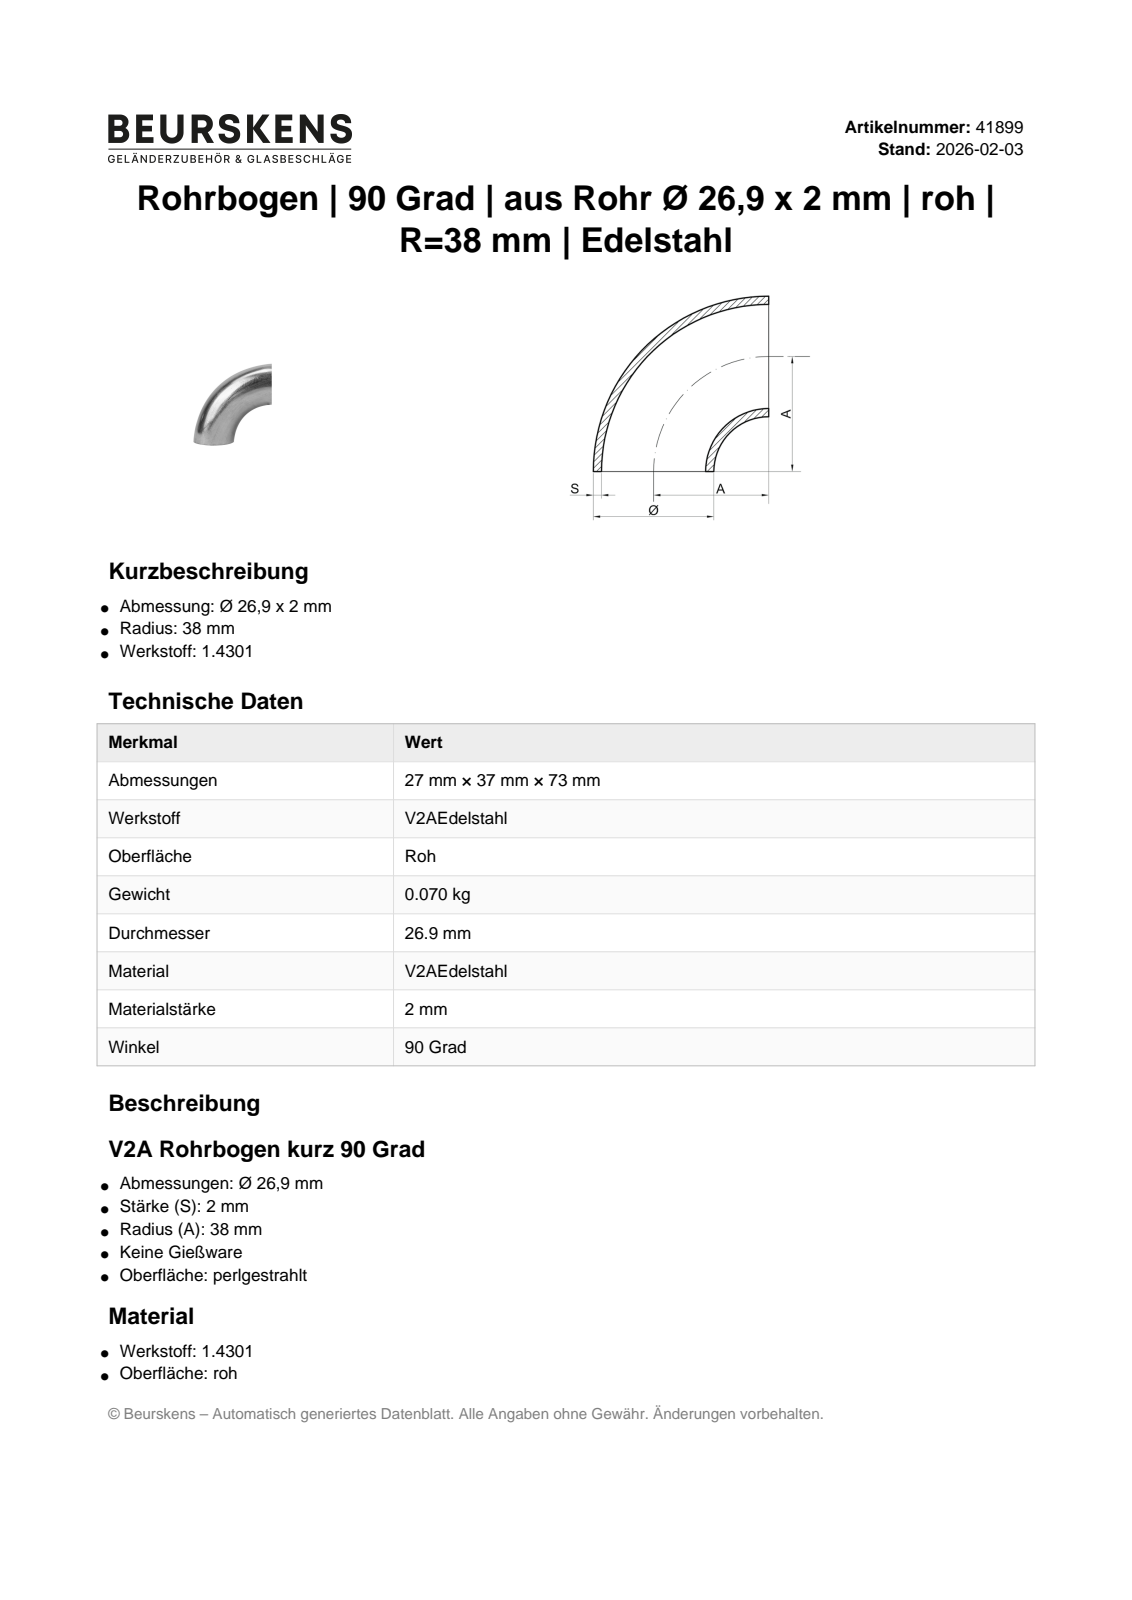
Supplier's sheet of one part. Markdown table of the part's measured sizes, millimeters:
| quantity | value |
| --- | --- |
| part name | 41899 |
| STEP written by | Autodesk Inventor 2022 (AUTOMOTIVE_DESIGN) |
| units | millimeters |
| bodies | 1 solid, 4 faces (2 planar, 0 cylindrical, 2 other) |
| overall size | 51.45 × 51.45 × 26.9 |
| volume | 9 338 mm³ |
| surface area | 9 651 mm² |
